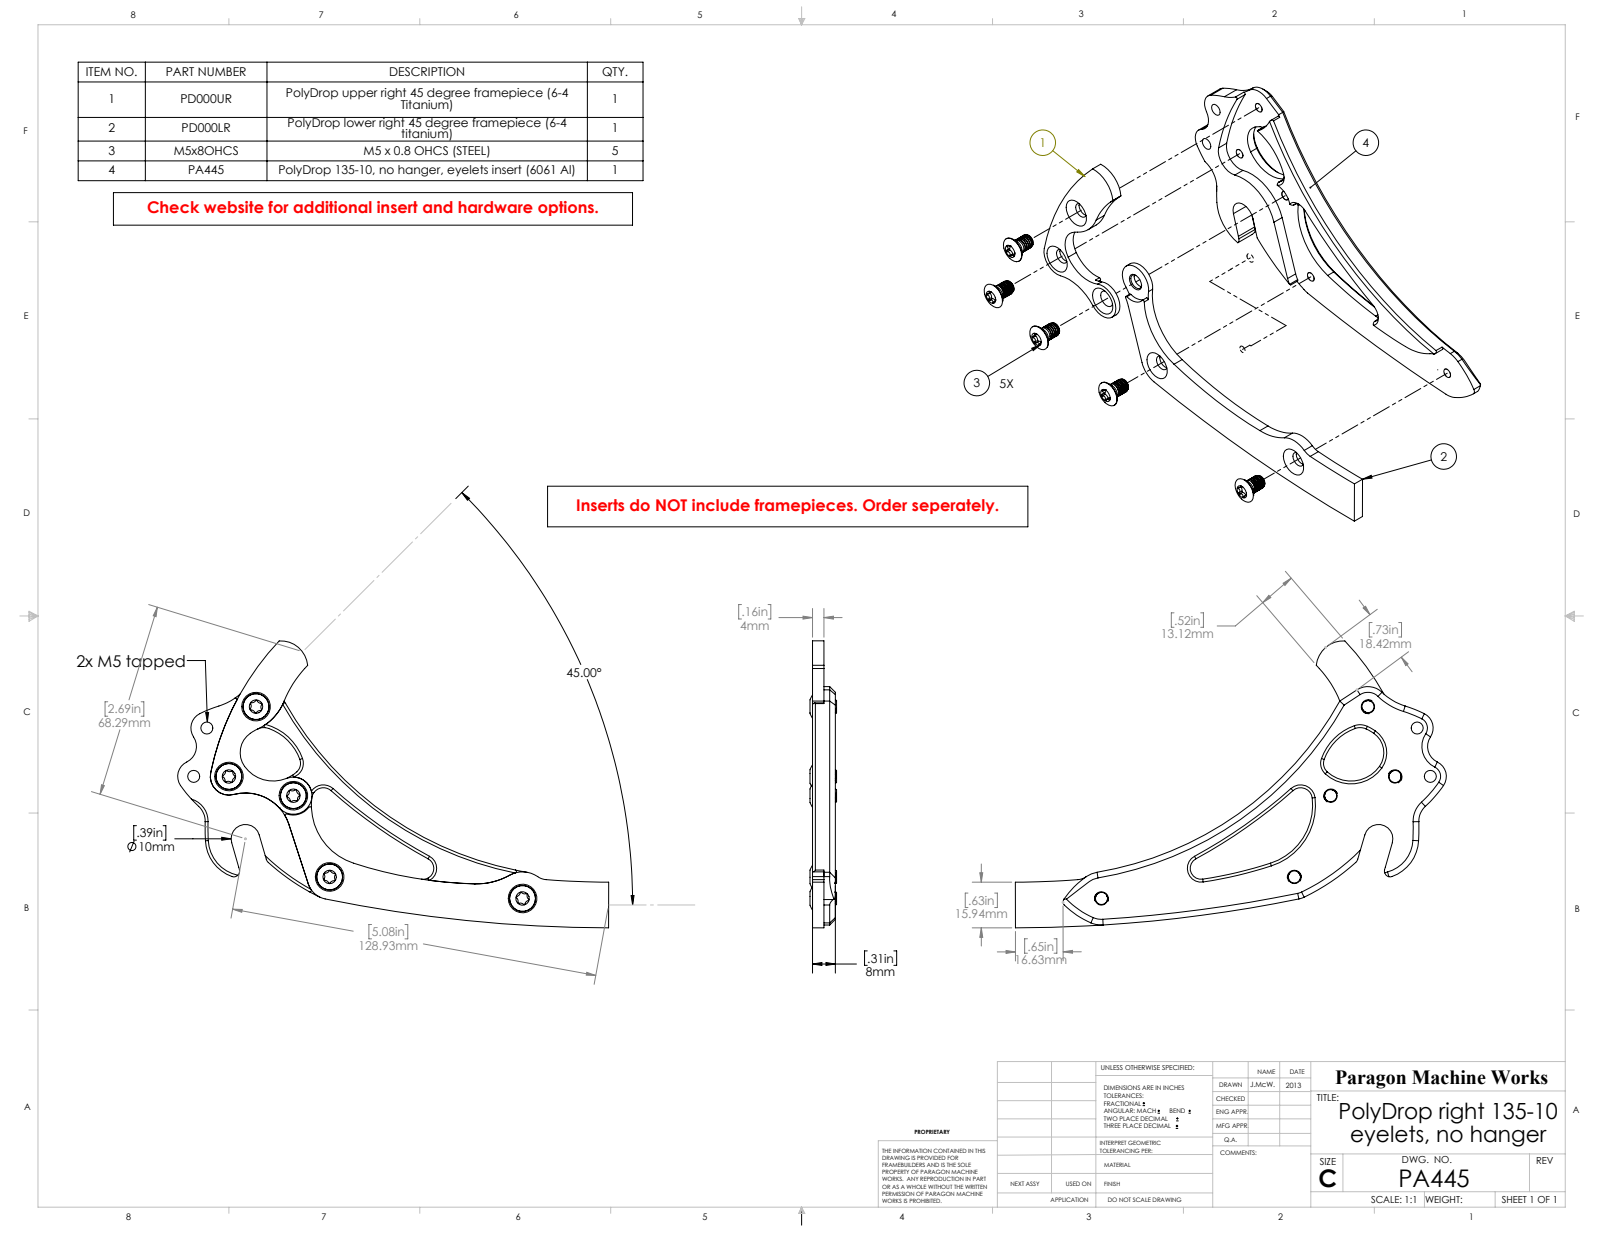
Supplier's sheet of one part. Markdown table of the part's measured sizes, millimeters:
| quantity | value |
| --- | --- |
| part name | PA445; M5x8OHCS_90258A246; PD000LR; PD000UR |
| STEP written by | SolidWorks 2012 (AUTOMOTIVE_DESIGN) |
| units | millimeters |
| bodies | 8 solids, 416 faces (29 planar, 221 cylindrical, 166 other) |
| overall size | 150.52 × 98.91 × 9.26 |
| volume | 31 209 mm³ |
| surface area | 19 887 mm² |
| round holes (diameter × count) | 5.3 × 5, 4.2 × 2 |
| round bosses / shafts (diameter × count) | 4.34 × 30, 5 × 5, 13 × 1 |
| partial cylindrical surfaces (radius × count) | 0.27 × 30, 1.54 × 30, 0.5 × 12, 2.17 × 5, 5 × 3, 5.59 × 2, 6 × 2, 7 × 2 |
| main face-to-face distances | 4, 8, 1.75, 2.25, 5.75, 6.25, 0.5, 0.4, 4.4, 6.15 |
| hole center spacings | 12.31, 17.51, 18.59, 18.73, 23.49, 26.16, 31.06, 32.68 |
